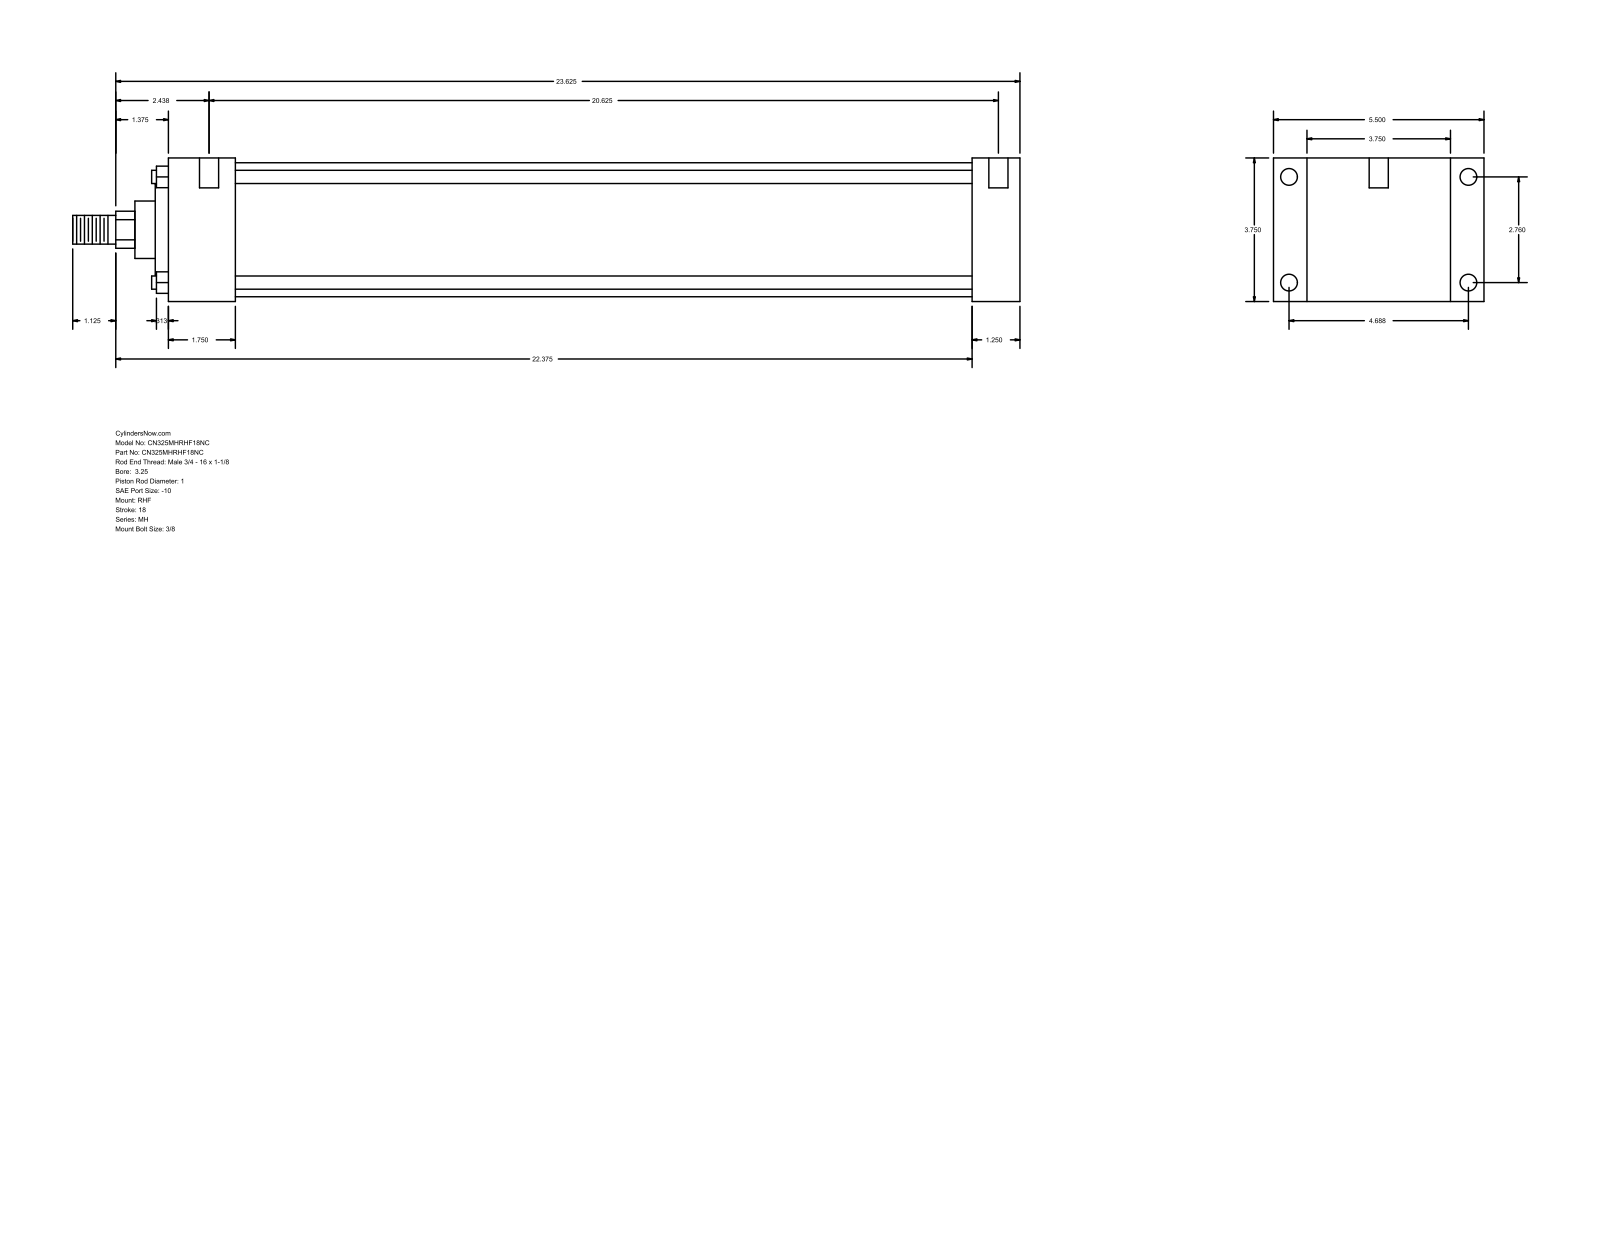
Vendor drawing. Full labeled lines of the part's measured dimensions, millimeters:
Part name (STEP PRODUCT): MH_RHF__0325_1
STEP written by: GSSL Pune (CONFIG_CONTROL_DESIGN)
Units: millimetres
Bodies: 0 solids, 90 faces (61 planar, 29 cylindrical, 0 other)
Overall size (bounding box): 628.65 × 139.7 × 95.25
Round holes (diameter × count): ⌀5.56 ×4, ⌀11.13 ×4, ⌀12.7 ×2
Round bosses / shafts (diameter × count): ⌀8.76 ×4, ⌀88.9 ×1, ⌀60.33 ×1, ⌀38.1 ×1, ⌀25.4 ×1, ⌀19.05 ×1
Partial cylindrical surfaces — rounded edges, fillets, slot ends (radius × count): R12.29 ×1
Main face-to-face distances: 95.24, 31.75, 22.23, 117.47, 533.41, 565.16, 139.7, 44.46, 488.95, 520.7
Hole centre spacings: 70.1, 119.06, 138.16, 530.22, 1.58, 4.76, 523.88, 525.46
